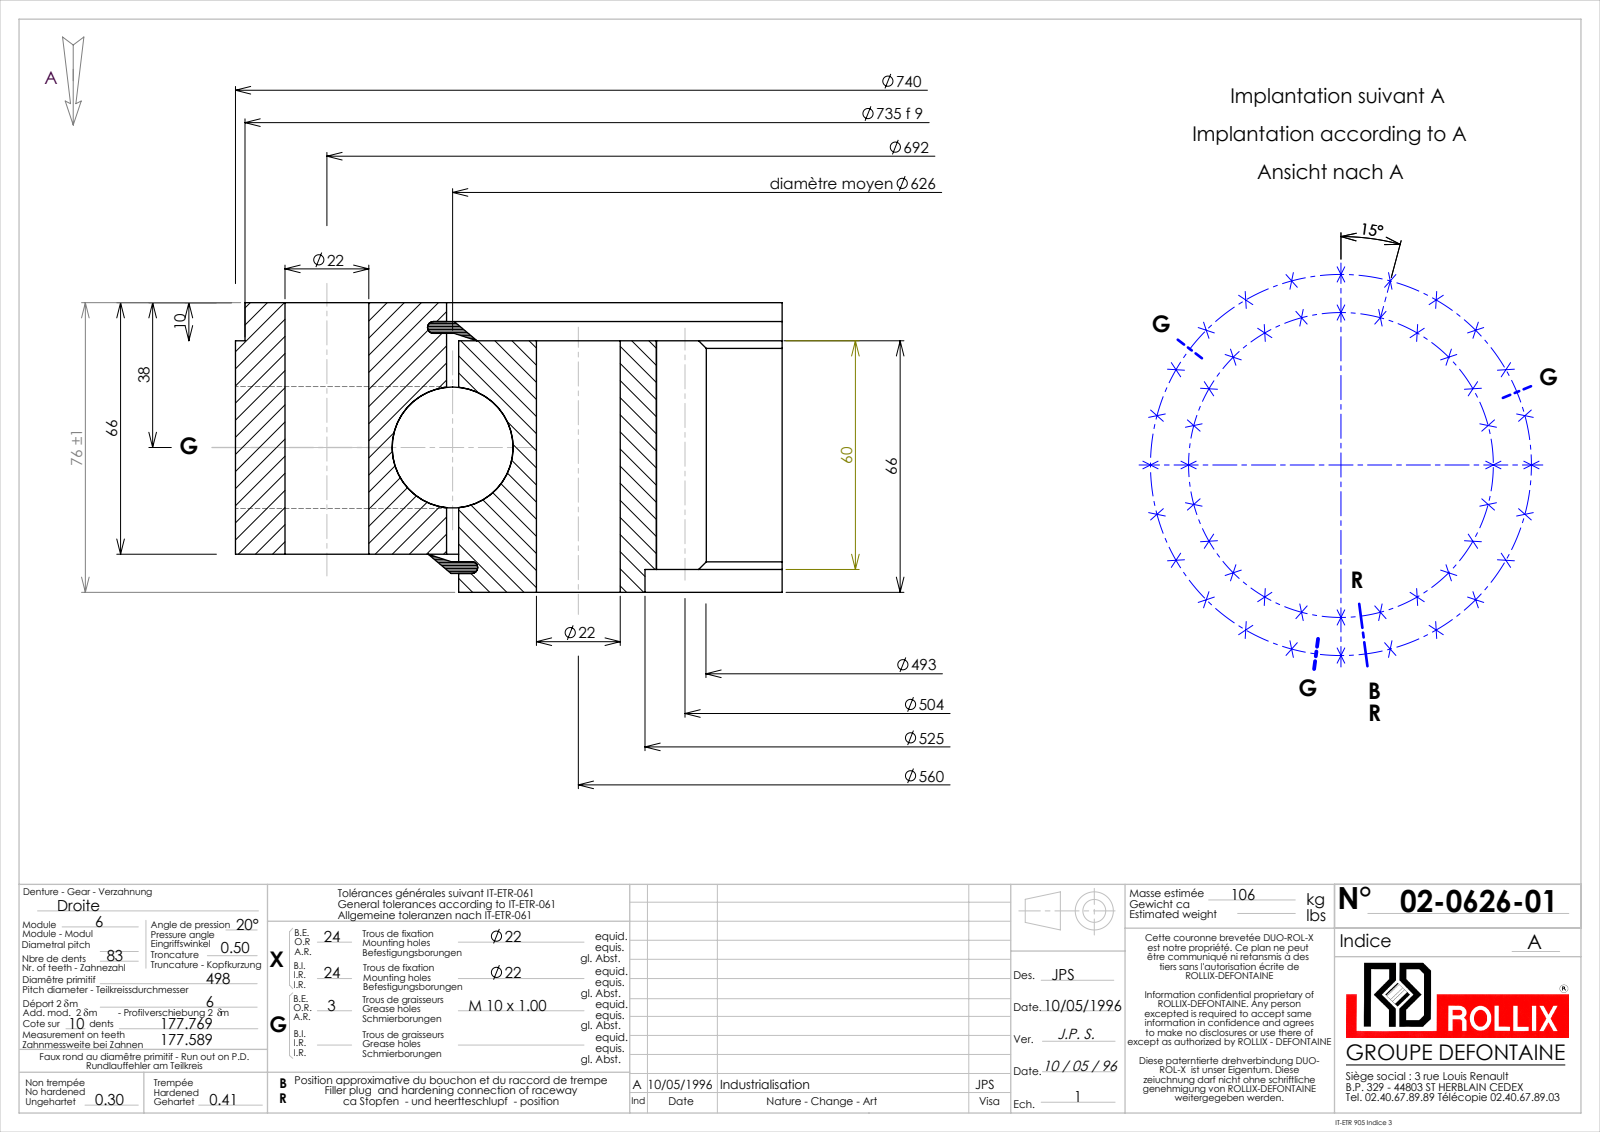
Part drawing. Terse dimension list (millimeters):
name: 02-0626-01
written by: SolidWorks 2016 (CONFIG_CONTROL_DESIGN)
unit: mm
bodies: 5 solids, 662 faces (180 planar, 287 cylindrical, 195 other)
size: 740 × 740 × 76
volume: 12 100 000 mm³; area: 1 452 000 mm²
holes: 48× ⌀22, 3× ⌀9, 1× ⌀525, 1× ⌀629.17, 1× ⌀629.18
bosses: 1× ⌀740, 1× ⌀735, 1× ⌀622.83
rounds: 1× R246.5, 1× R259.5
face distances: 66, 10, 56, 76, 4.95, 71.05, 5.05, 61.05, 8.05, 67.95
hole spacings: 280, 144.94, 214.3, 340.91, 395.98, 444.28, 540.92, 555.21
